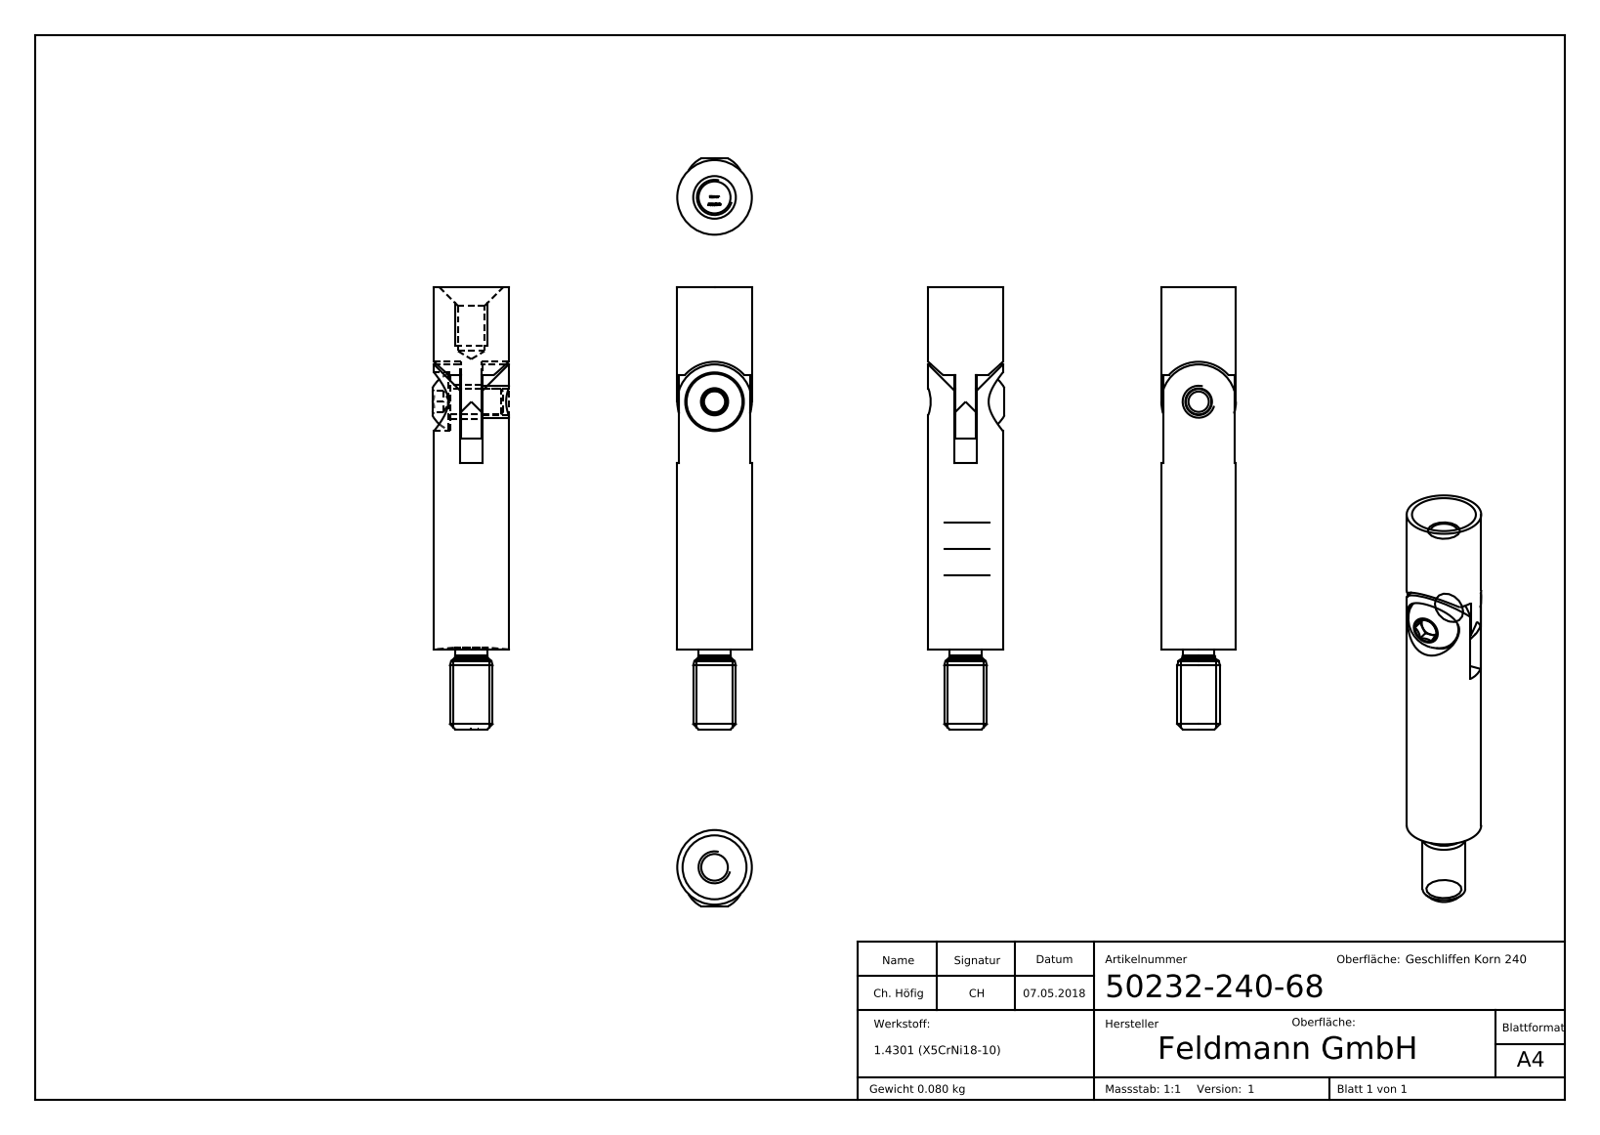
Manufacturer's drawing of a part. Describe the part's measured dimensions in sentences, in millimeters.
The part is named "ISO7380 -M6x10_DIN7380 M6x10; 50232-240-68; 50232-240-68 Teil1; 50232-240-68 Teil2_50232-240-68 Teil2 (+3 more)". Its 3-D file was written by "SolidWorks 2018 (CONFIG_CONTROL_DESIGN)". It is 3 solids with 323 faces: 156 planar, 16 cylindrical and 151 other. Overall it measures 87 by 17.35 by 14 millimeters. Its volume is 10 171 cubic millimeters and its surface area 5 353 square millimeters. Round holes: 2 of diameter 5, 1 of diameter 6.5, 1 of diameter 11. Round bosses or shafts: 2 of diameter 14, 1 of diameter 10.5, 1 of diameter 8, 1 of diameter 6, 1 of diameter 4.77. Partial cylindrical surfaces (rounded edges, fillets, slot ends): 1 of radius 7.5. The main face-to-face distances are 4.05, 4.1, 4, 6.05, 1.95, 2, 6, 33, 50, 83.
